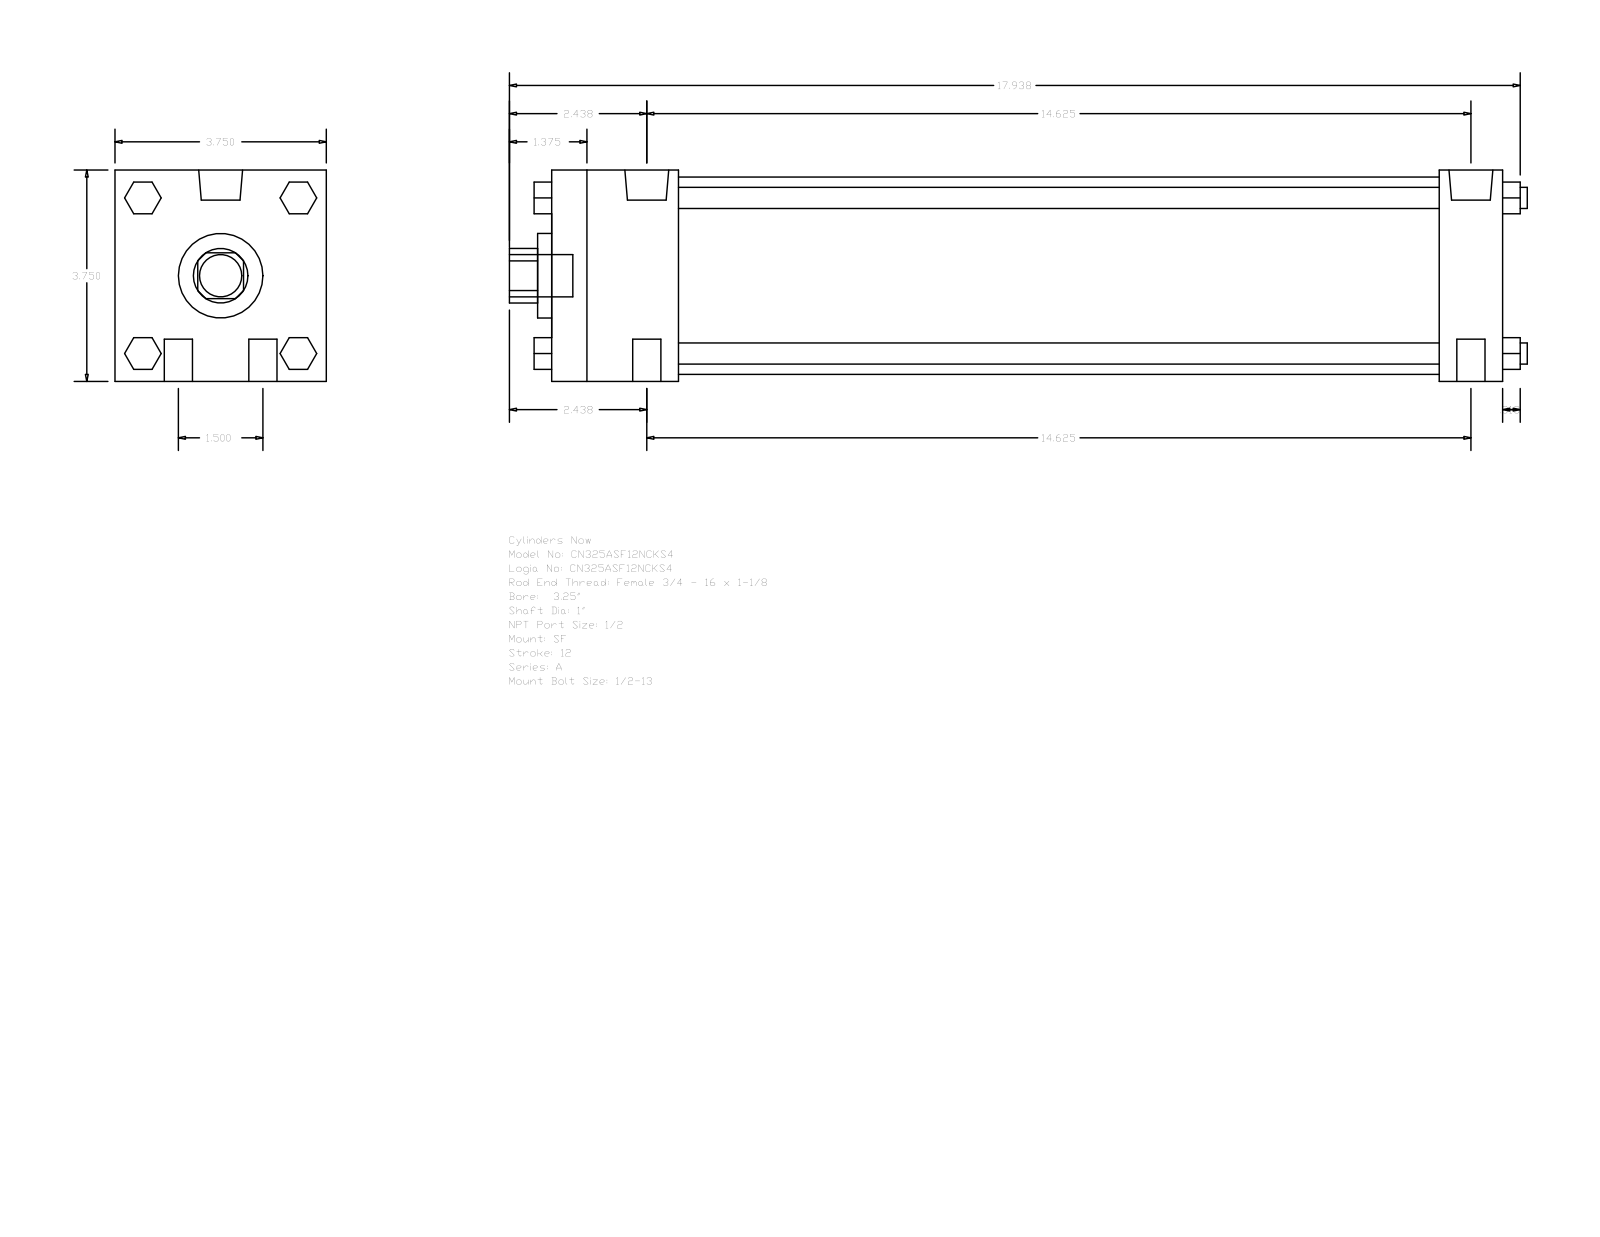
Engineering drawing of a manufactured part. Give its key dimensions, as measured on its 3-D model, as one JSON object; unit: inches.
{"part_name": "A_SF__0325_1", "step_written_by": "GSSL Pune (CONFIG_CONTROL_DESIGN)", "units": "inches", "bodies": {"solids": 0, "faces": 124, "planar": 94, "cylindrical": 30, "other": 0}, "overall_size": [18.063, 3.75, 3.75], "round_holes": [[1, 1], [1.5, 1], [3.5, 1]], "round_bosses_or_shafts": [[0.5, 4], [0.375, 4], [0.778, 2], [0.344, 2], [0.75, 1]], "partial_cylinders_radius": [[0.484, 1]], "face_to_face_distances": [3.75, 16.875, 15.75, 1.125, 2.25, 13.5, 14.625, 0.562, 1.38, 2.39]}
